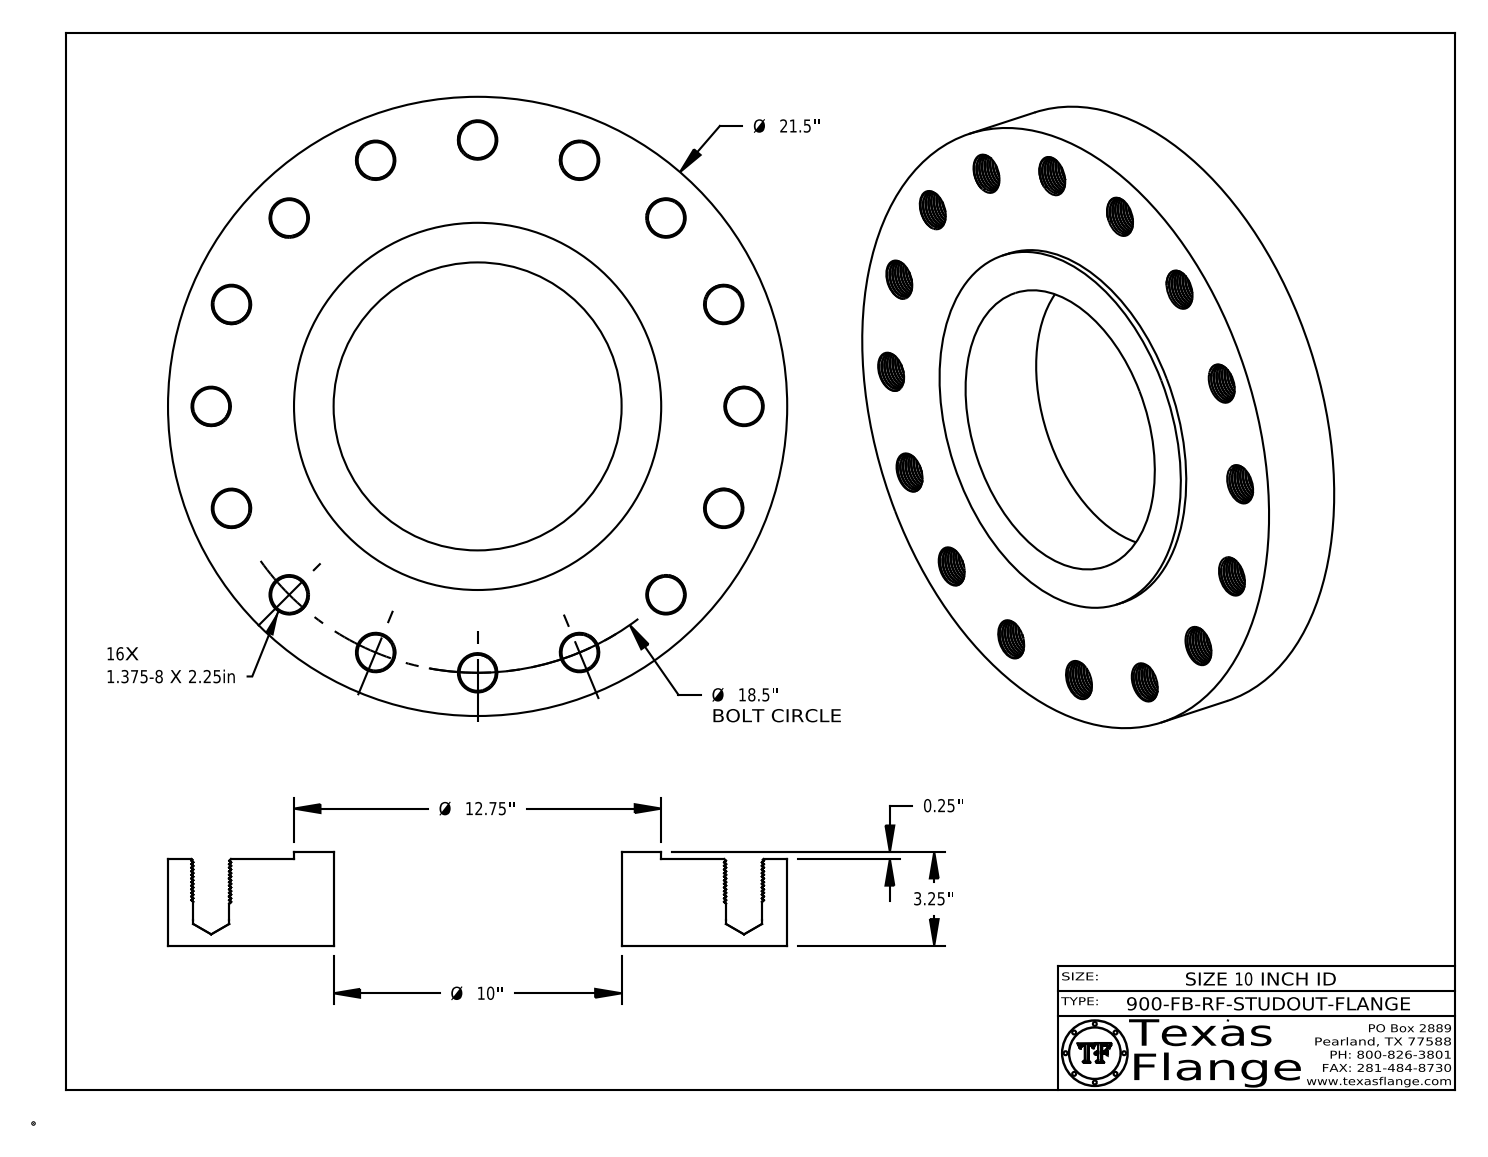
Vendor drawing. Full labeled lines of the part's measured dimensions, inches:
Part name (STEP PRODUCT): 10-900-FB-RF-STUDOUT-FLANGE
STEP written by: CATIA V5 STEP AP214 (AUTOMOTIVE_DESIGN)
Units: inches
Bodies: 1 solid, 1706 faces (368 planar, 442 cylindrical, 896 other)
Overall size (bounding box): 21.5 × 21.5 × 3.25
Volume: 816.2 in³ · Surface area: 1 071 in²
Round holes (diameter × count): ⌀1.25 ×16, ⌀1 ×1, ⌀10 ×1
Round bosses / shafts (diameter × count): ⌀0.061 ×8, ⌀21.5 ×1, ⌀12.75 ×1, ⌀0.788 ×1
Main face-to-face distances: 3, 0.25, 3.25, 3.235, 2.985, 0.015, 0.298, 0.293, 0.054, 0.248
Hole centre spacings: 15.382, 7.08, 9.25, 13.081, 3.609, 3.609, 10.278, 10.278
